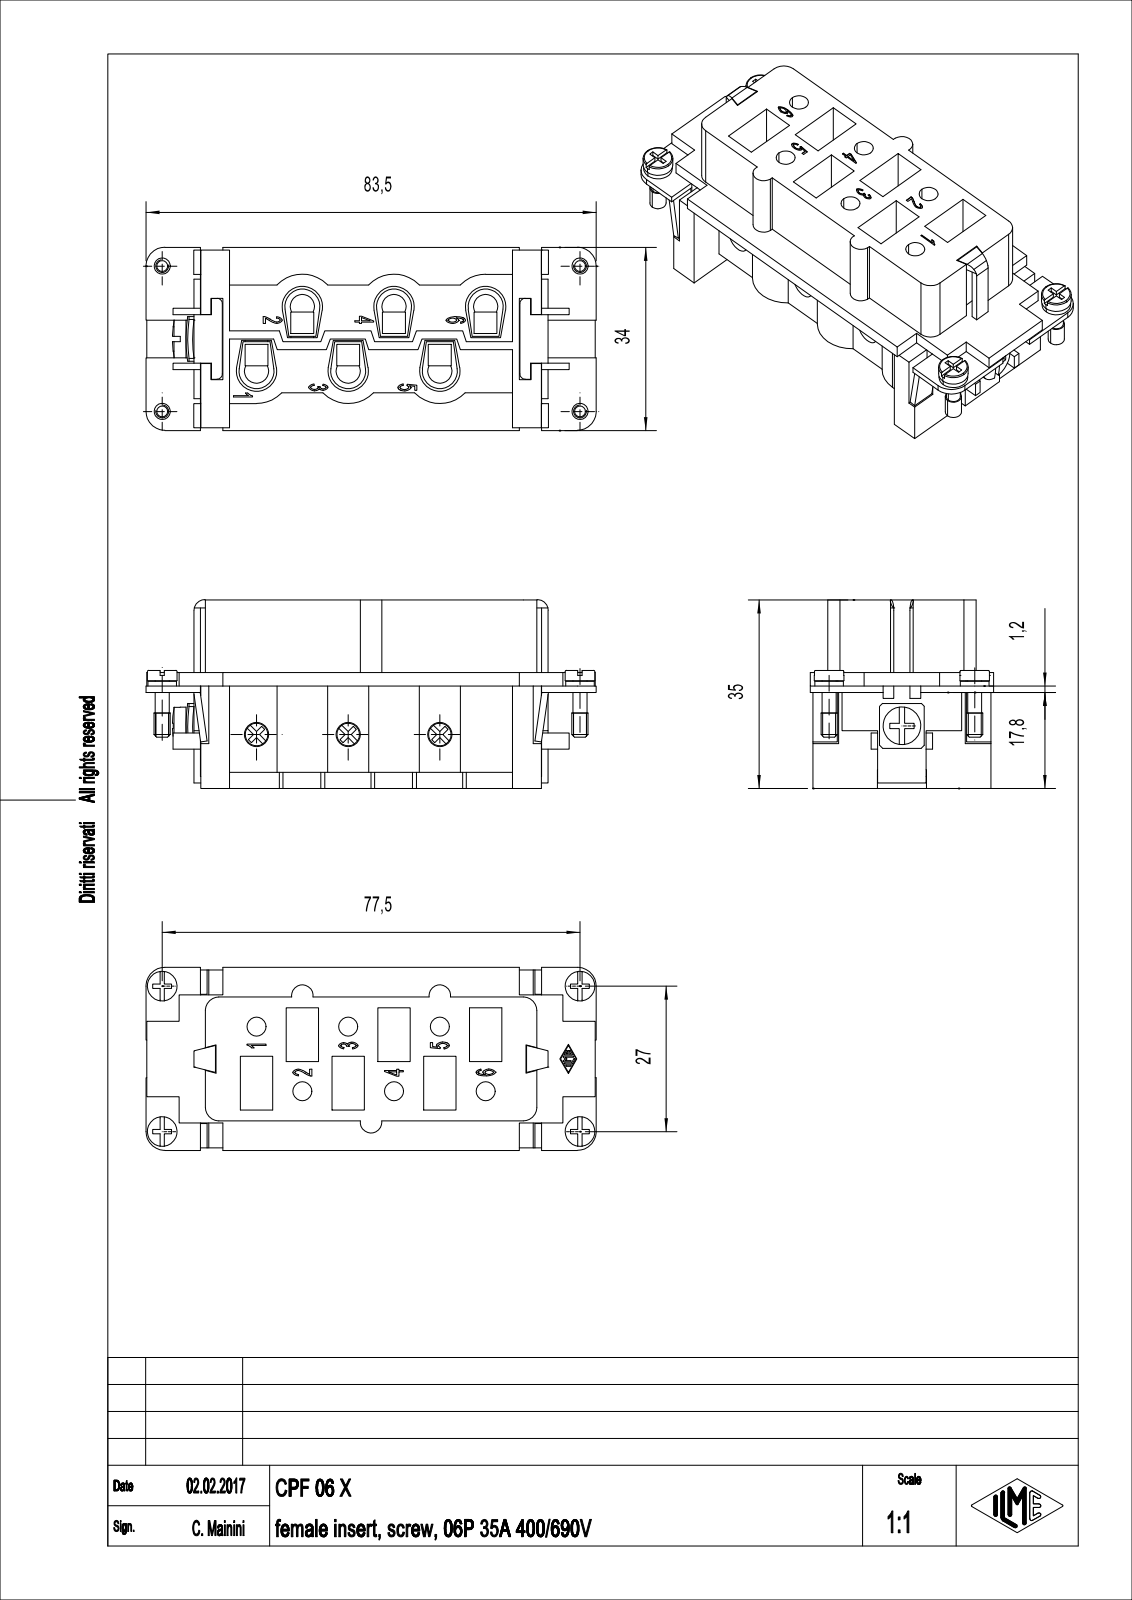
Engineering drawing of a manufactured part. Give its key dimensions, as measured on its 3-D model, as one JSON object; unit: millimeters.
{"part_name": "CPF_06_X", "step_written_by": "PTC Creo Elements/Direct Modeling 19.0E 27-Jun-2016 (C) Parametric Technology GmbH (AUTOMOTIVE_DESIGN)", "units": "millimeters", "bodies": {"solids": 3, "faces": 957, "planar": 645, "cylindrical": 168, "other": 144}, "overall_size": [83.5, 35, 34], "volume_mm3": 43813, "surface_area_mm2": 25380, "round_holes": [[4.5, 12], [3.5, 6], [3.24, 1]], "round_bosses_or_shafts": [[4.2, 6], [5.5, 4], [5.3, 4], [3, 4], [2.6, 4], [7, 1]], "partial_cylinders_radius": [[0.1, 14], [3.25, 6], [3.75, 6], [6.5, 6], [2, 5], [1, 4], [2.5, 4], [3.5, 4]], "face_to_face_distances": [16, 2.5, 12, 0.5, 17, 23, 13.5, 1.5, 1.2, 8.5], "hole_center_spacings": [17, 8.5, 14.71, 34, 25.5, 28.18, 42.5, 44.16]}
